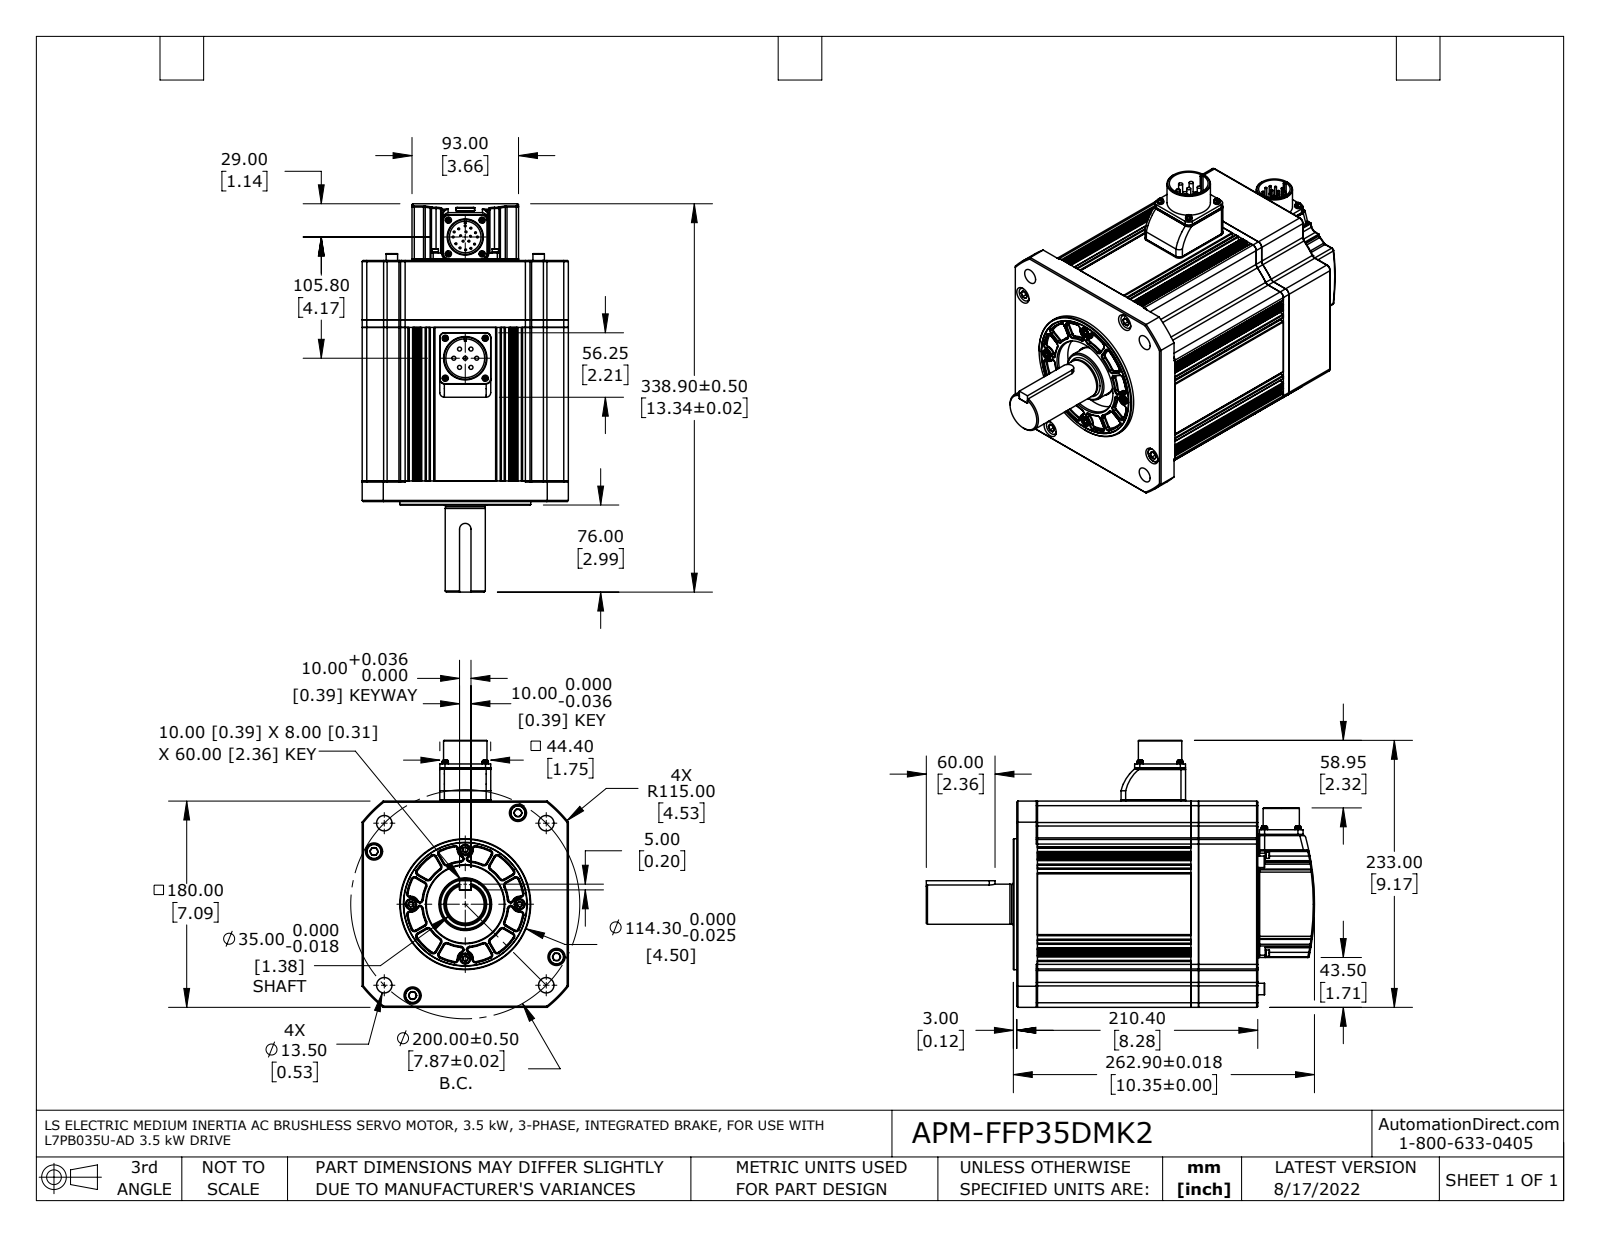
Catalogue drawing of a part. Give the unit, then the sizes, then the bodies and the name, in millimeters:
Units: millimetres
Overall size (bounding box): 338.9 × 233 × 180
Round holes (diameter × count): ⌀3 ×17, ⌀2.5 ×9, ⌀6 ×8, ⌀9.5 ×8, ⌀6.8 ×6, ⌀3 ×4, ⌀3.5 ×4, ⌀3.6 ×4, ⌀3.7 ×4, ⌀3.7 ×4, ⌀5 ×4, ⌀9 ×4
Round bosses / shafts (diameter × count): ⌀1.6 ×17, ⌀5.4 ×8, ⌀3.5 ×7, ⌀13.2 ×4, ⌀13 ×4, ⌀8.5 ×4, ⌀8 ×4, ⌀5.5 ×4
Partial cylindrical surfaces — rounded edges, fillets, slot ends (radius × count): R0.5 ×124, R2.5 ×56, R4 ×24, R1 ×22, R2 ×17, R4.5 ×12, R6.5 ×4, R0.3 ×2
Main face-to-face distances: 134, 6.7, 140.7, 180, 1, 10, 18, 8, 33.5, 146.5
Hole centre spacings: 32.6, 33.4, 34.1, 74.4, 92, 137.7, 26.3, 56.1
Volume: 6 450 000 mm³ · Surface area: 585 800 mm²
Bodies: 64 solids, 2511 faces (820 planar, 949 cylindrical, 742 other)
Part name (STEP PRODUCT): FMP18GA003G02_Out Line(APM-FFP35D_K2) r1 nc fxt
STEP written by: SolidWorks 2017 (AUTOMOTIVE_DESIGN)
